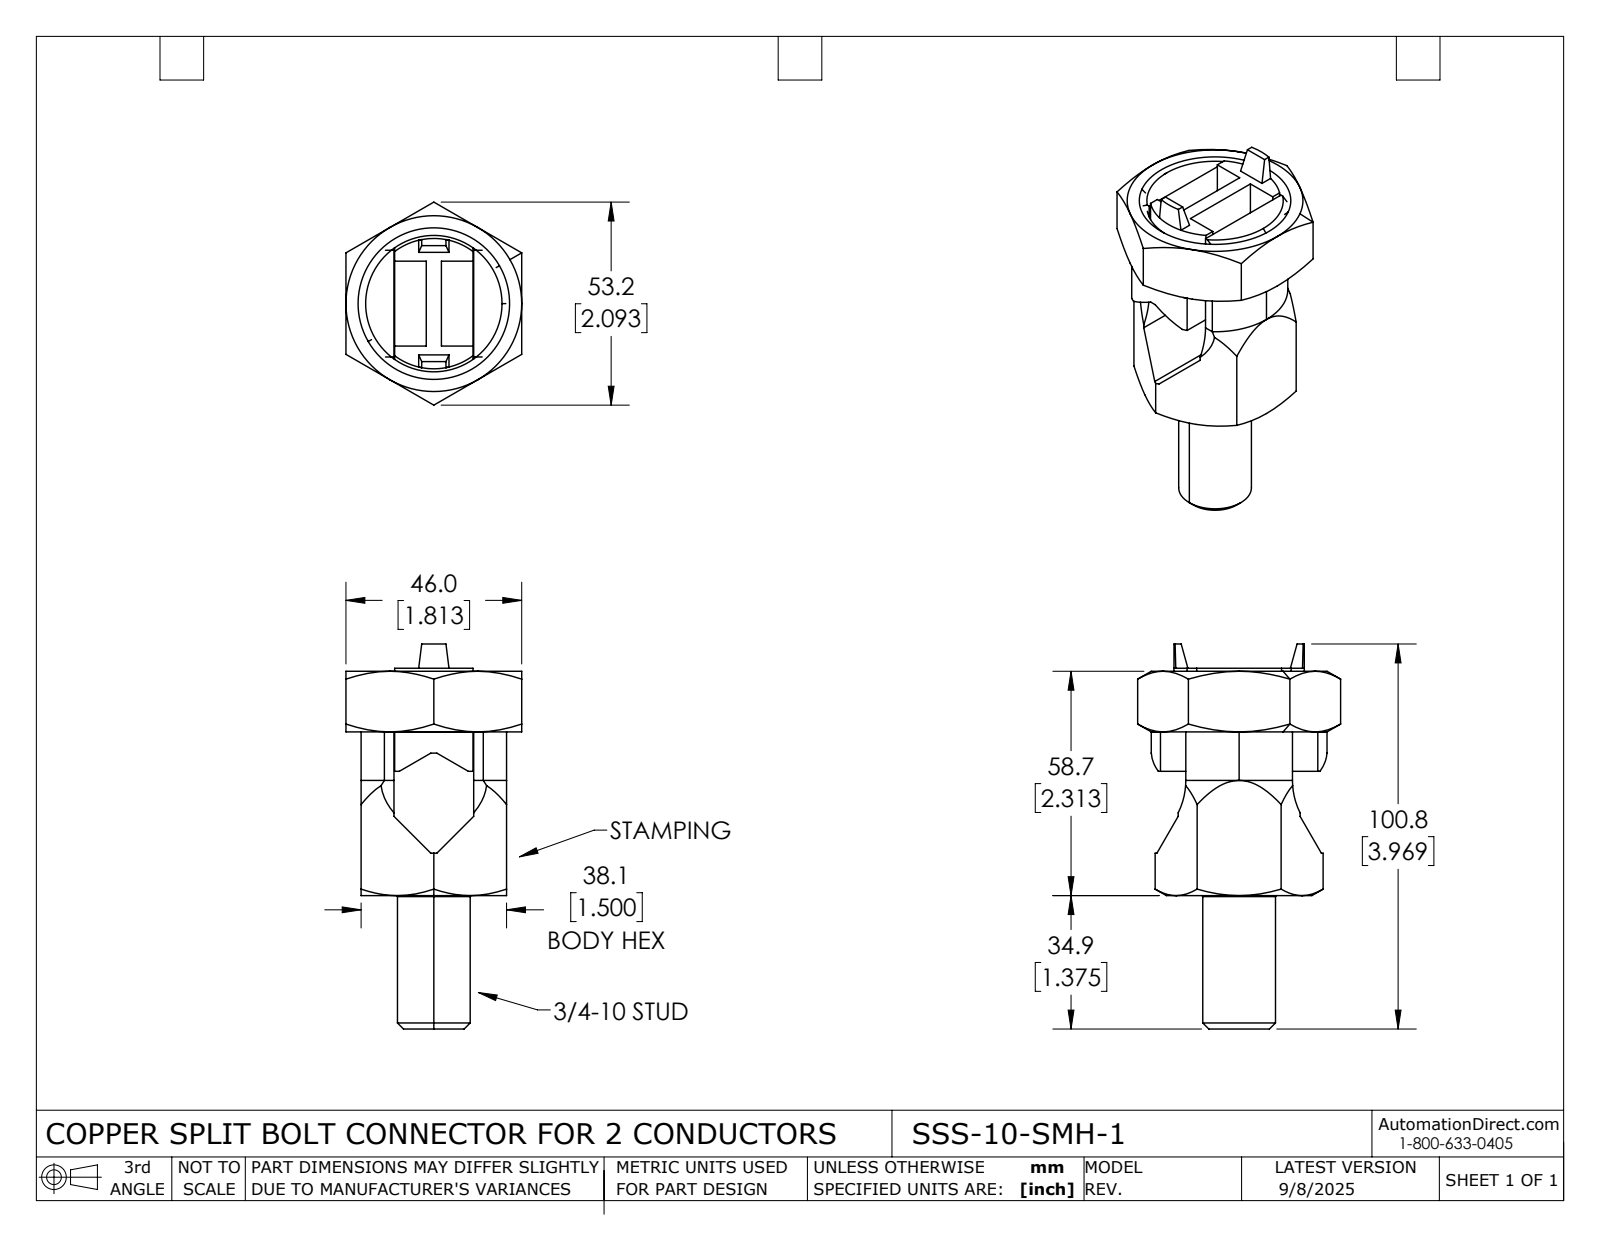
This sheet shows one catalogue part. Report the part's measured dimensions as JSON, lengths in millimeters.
{"part_name": "SSS-10-SMH-1", "step_written_by": "SolidWorks 2024 (AUTOMOTIVE_DESIGN)", "units": "millimeters", "bodies": {"solids": 3, "faces": 106, "planar": 53, "cylindrical": 15, "other": 38}, "overall_size": [100.8, 53.2, 46.1], "volume_mm3": 70190, "surface_area_mm2": 23190, "round_holes": [[35.7, 1]], "round_bosses_or_shafts": [[19.1, 1]], "partial_cylinders_radius": [[19.1, 3], [17.1, 1], [23, 1]], "face_to_face_distances": [4, 42.1, 38.1, 8.6, 29.5, 46.1, 20.9, 17.1, 21, 8.5]}
